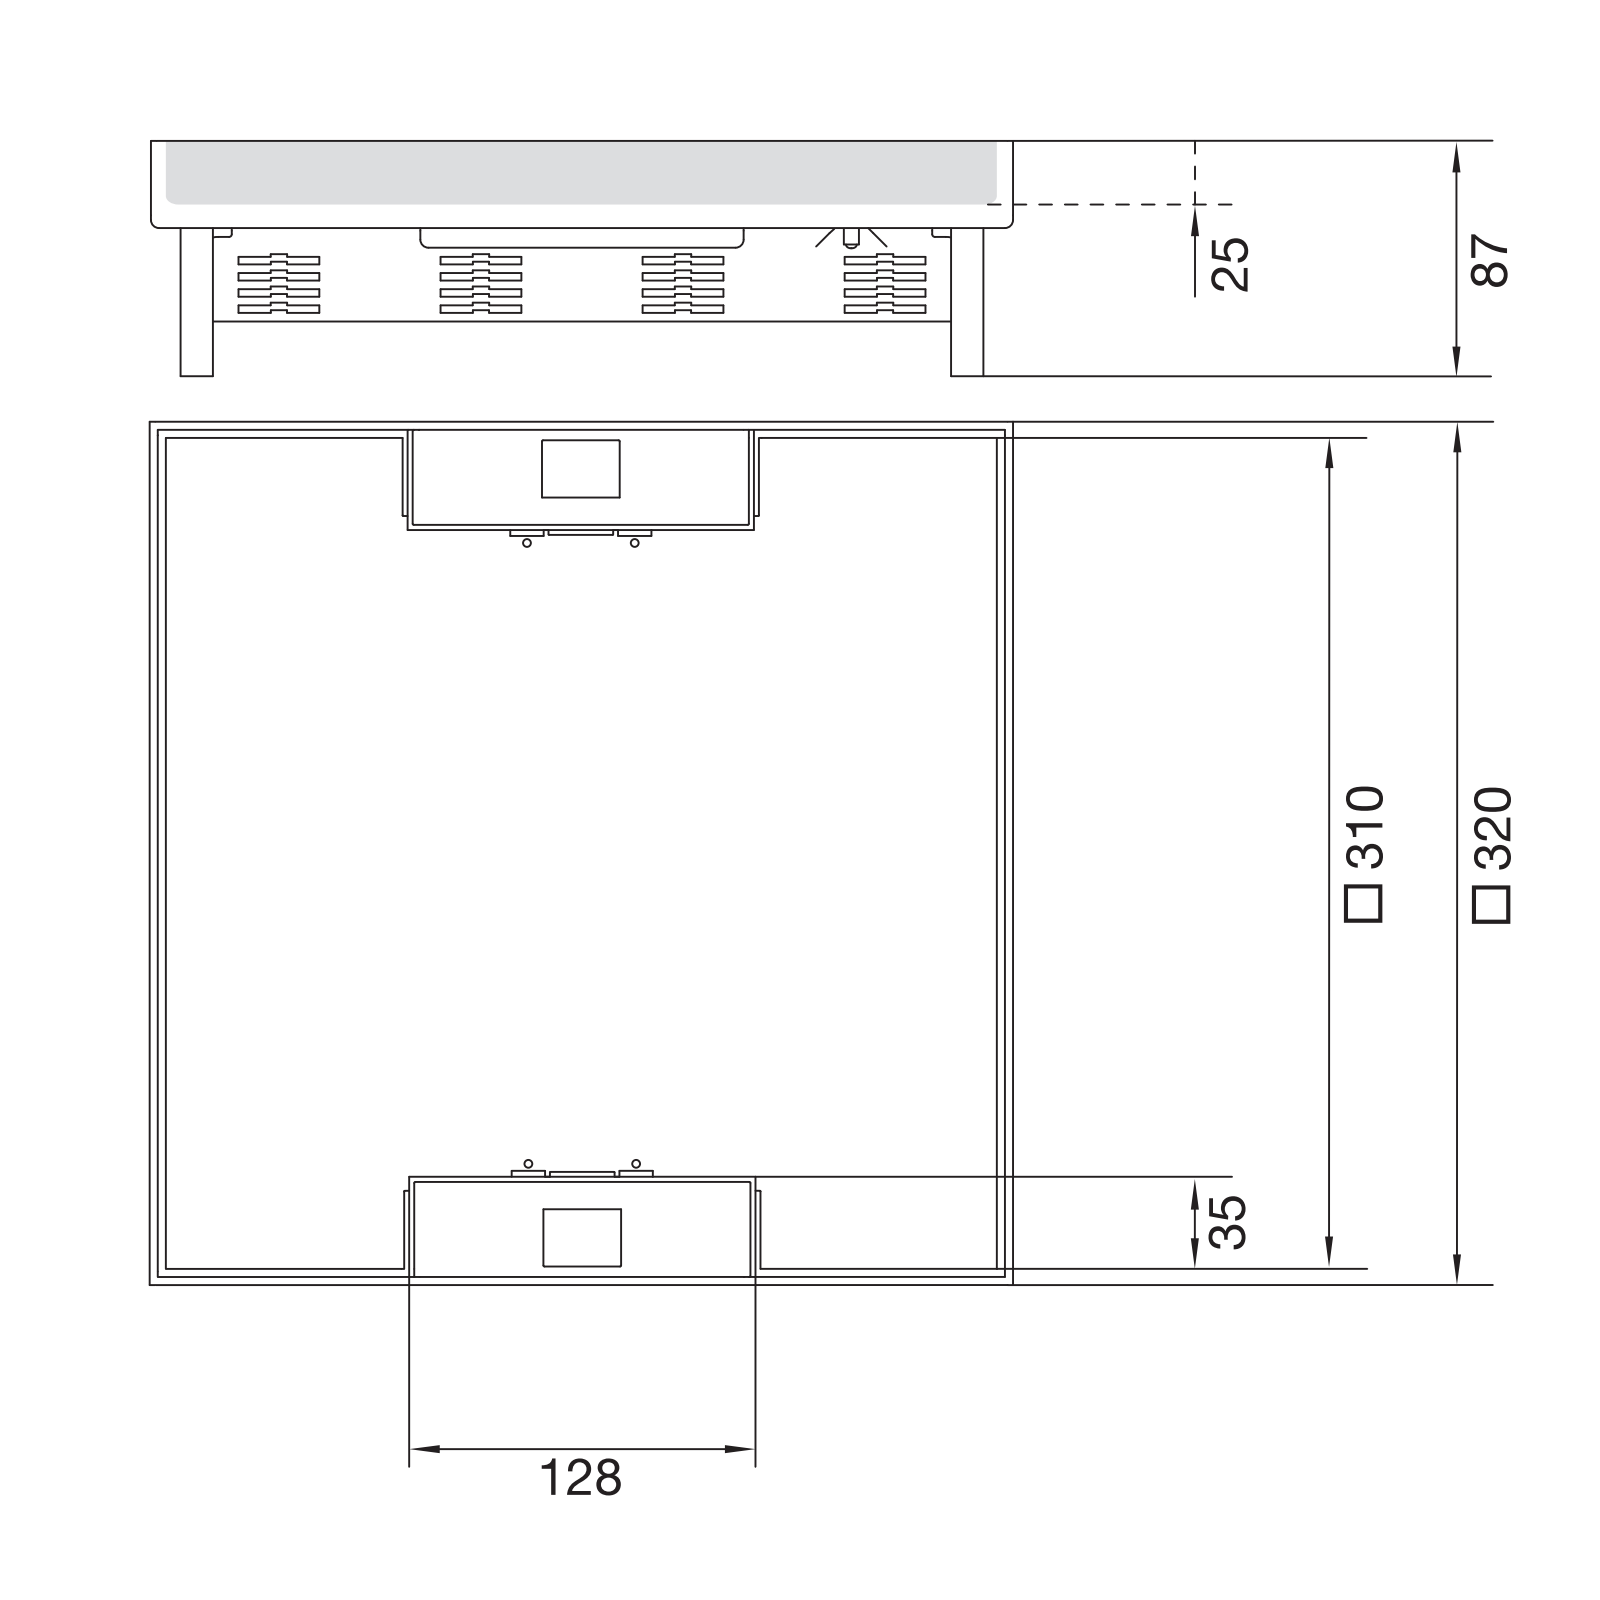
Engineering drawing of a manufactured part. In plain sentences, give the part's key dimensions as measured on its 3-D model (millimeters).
The part is named "T-00645; U09001; T-00834_ASM; T-00652 (+6 more)". Its 3-D file was written by "CREO PARAMETRIC BY PTC INC, 2022024 (AUTOMOTIVE_DESIGN)". It is 8 solids with 334 faces: 268 planar, 66 cylindrical and 0 other. Overall it measures 320 by 320 by 87 millimeters. Its volume is 445 366 cubic millimeters and its surface area 462 049 square millimeters. Round holes: 4 of diameter 2.7. Round bosses or shafts: 4 of diameter 12, 4 of diameter 9.85. Partial cylindrical surfaces (rounded edges, fillets, slot ends): 10 of radius 1, 10 of radius 3, 6 of radius 10, 2 of radius 5, 2 of radius 6.6. The main face-to-face distances are 2, 3, 5, 315, 318, 45.3, 272.7, 7, 1, 317. The hole center spacings are 40, 230, 233.45.
